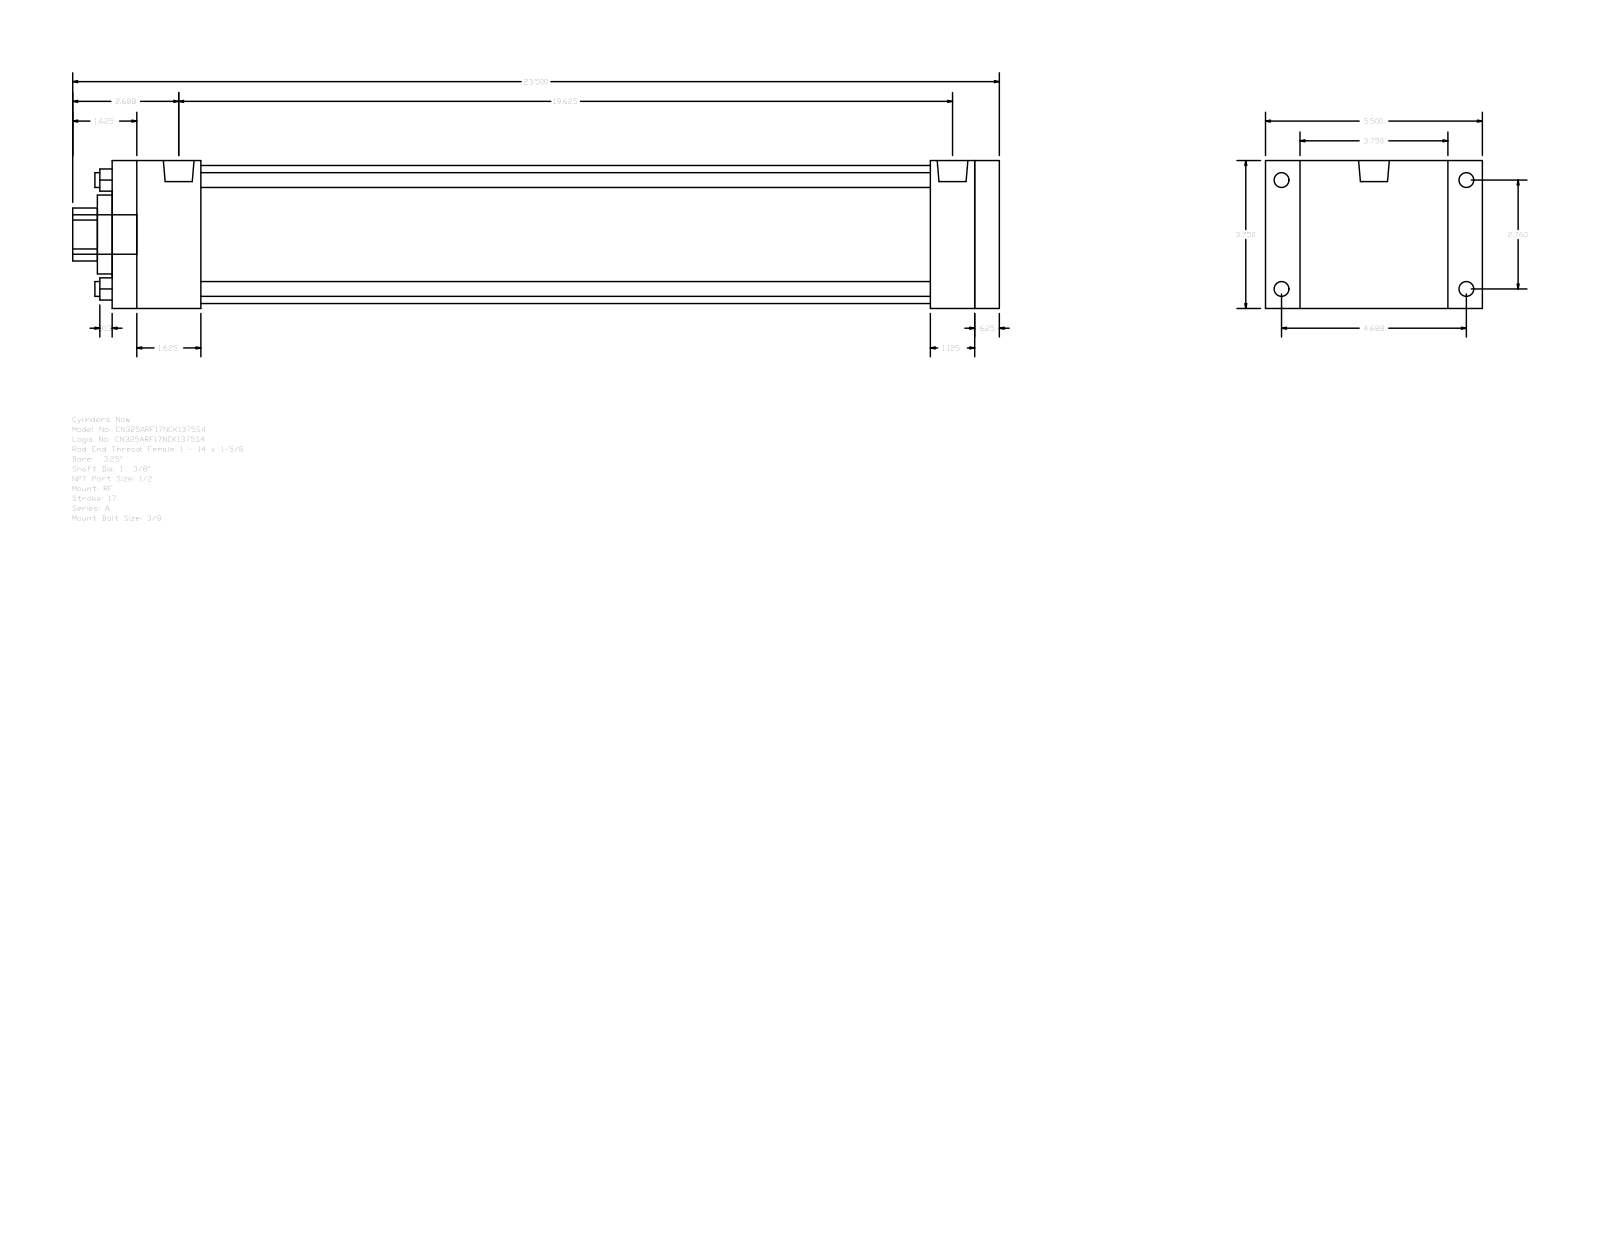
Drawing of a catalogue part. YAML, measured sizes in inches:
part_name: "A_RF__0325_1.375"
step_written_by: "GSSL Pune (CONFIG_CONTROL_DESIGN)"
units: inches
bodies: {solids: 0, faces: 92, planar: 64, cylindrical: 28, other: 0}
overall_size: [23.5, 5.5, 3.75]
round_holes:
  - {diameter: 0.375, count: 4}
  - {diameter: 1.375, count: 1}
  - {diameter: 2, count: 1}
  - {diameter: 3.5, count: 1}
round_bosses_or_shafts:
  - {diameter: 0.375, count: 4}
  - {diameter: 0.344, count: 4}
  - {diameter: 0.778, count: 2}
  - {diameter: 1, count: 1}
partial_cylinders:
  - {radius: 0.672, count: 1}
face_to_face_distances: [3.75, 22.5, 0.625, 21.875, 0.875, 4.625, 1.125, 20.75, 1.75, 2.25]
hole_center_spacings: [1.952, 2.76, 3.903]
